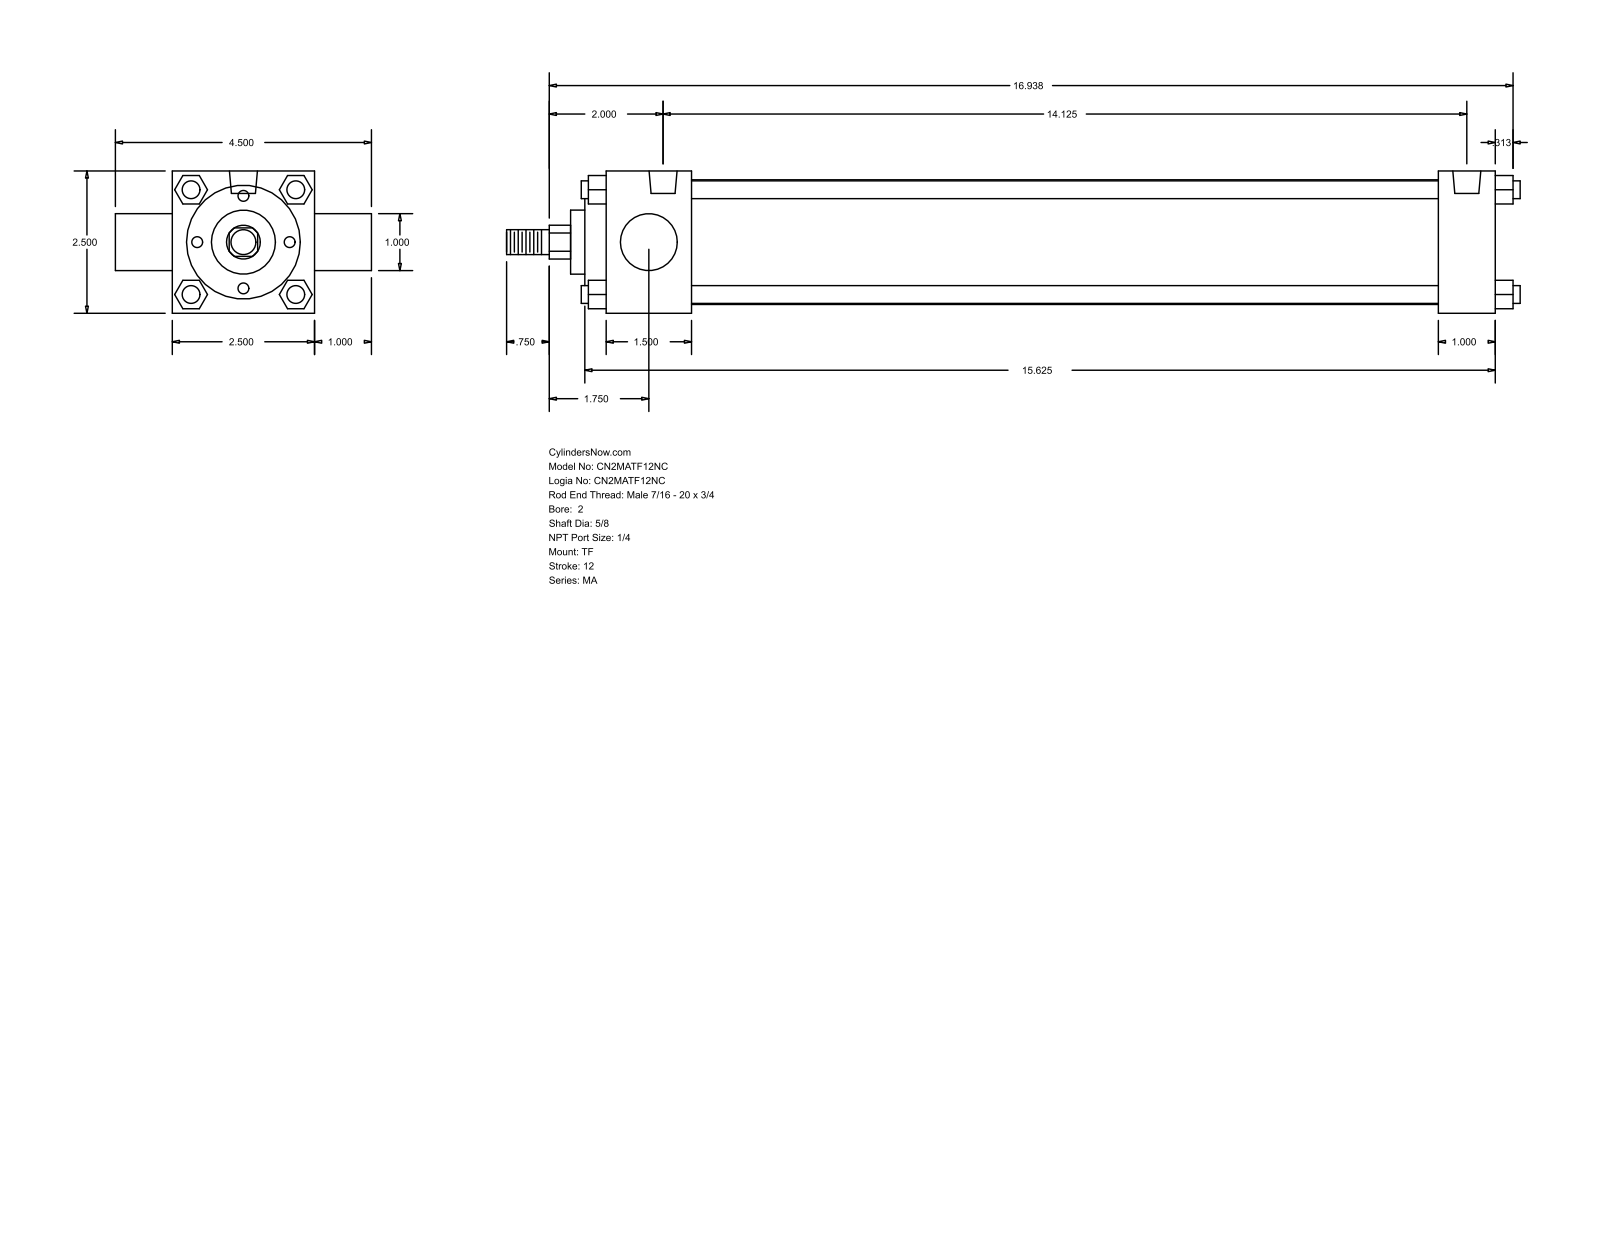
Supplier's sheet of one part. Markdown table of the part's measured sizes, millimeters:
| quantity | value |
| --- | --- |
| part name | MA_TF__0200_0.625 |
| STEP written by | GSSL Pune (CONFIG_CONTROL_DESIGN) |
| units | millimeters |
| bodies | 0 solids, 122 faces (93 planar, 29 cylindrical, 0 other) |
| overall size | 452.44 × 114.3 × 63.5 |
| round holes (diameter × count) | 7.94 × 3, 12.49 × 2 |
| round bosses / shafts (diameter × count) | 7.94 × 4, 55.63 × 1, 50.8 × 1, 28.57 × 1, 25.4 × 1, 15.88 × 1, 11.11 × 1 |
| partial cylindrical surfaces (radius × count) | 7.54 × 1 |
| main face-to-face distances | 63.5, 38.1, 12.7, 396.87, 371.48, 333.38, 358.77, 25.39, 9.52, 47.62 |
| hole center spacings | 358.77 |
